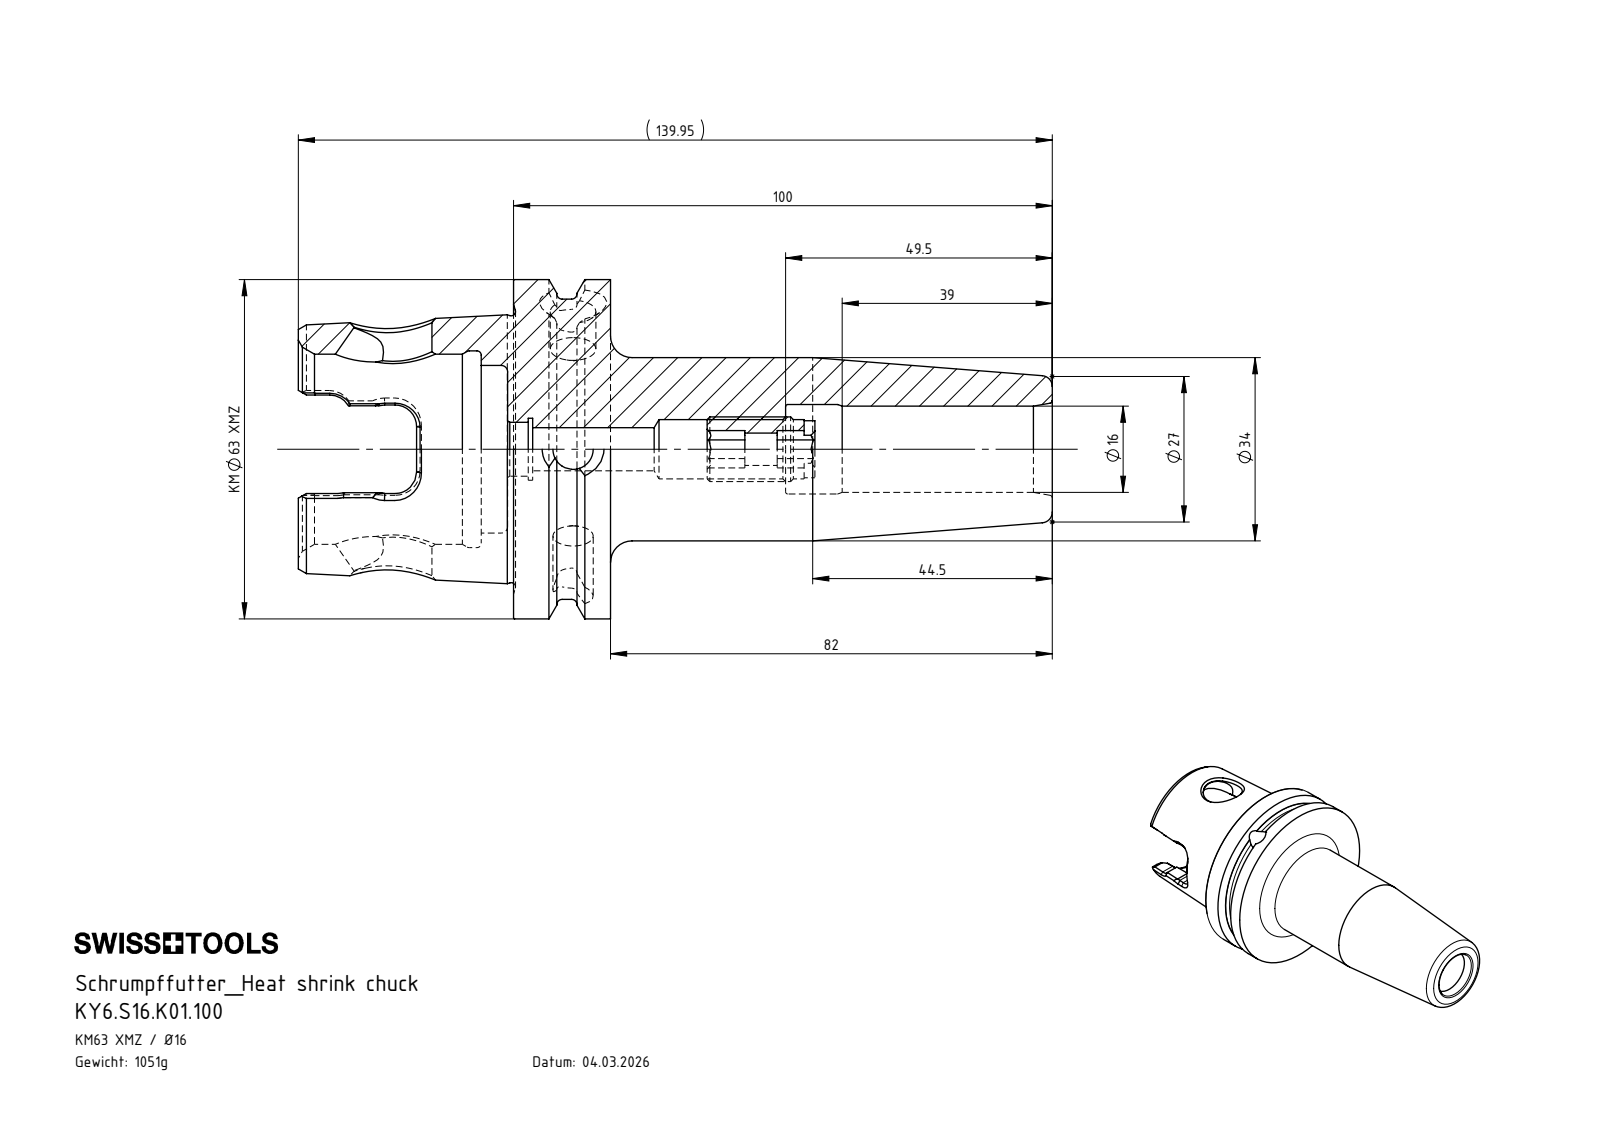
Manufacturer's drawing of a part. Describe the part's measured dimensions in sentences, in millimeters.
The part is named "KY6.S16.K01.100; KY6-S16.K01.100_A; ERU-AN5.K01.020_A". Its 3-D file was written by "SolidWorks 2022 (AUTOMOTIVE_DESIGN)". It is 2 solids with 213 faces: 79 planar, 37 cylindrical and 97 other. Overall it measures 139.95 by 62.95 by 62.95 millimeters. Its volume is 133 695 cubic millimeters and its surface area 32 625 square millimeters. Round holes: 2 of diameter 7.47, 1 of diameter 6, 1 of diameter 8, 1 of diameter 8.48, 1 of diameter 10, 1 of diameter 11, 1 of diameter 11.5, 1 of diameter 14.5, 1 of diameter 16, 1 of diameter 16.6, 1 of diameter 31.1, 1 of diameter 35.27. Round bosses or shafts: 1 of diameter 62.95, 1 of diameter 55.7, 1 of diameter 34, 1 of diameter 12. Partial cylindrical surfaces (rounded edges, fillets, slot ends): 6 of radius 4, 2 of radius 7.04. The main face-to-face distances are 18, 1.1, 19.1, 6, 4.9, 24, 33.95, 38.85, 39.95, 57.95.
